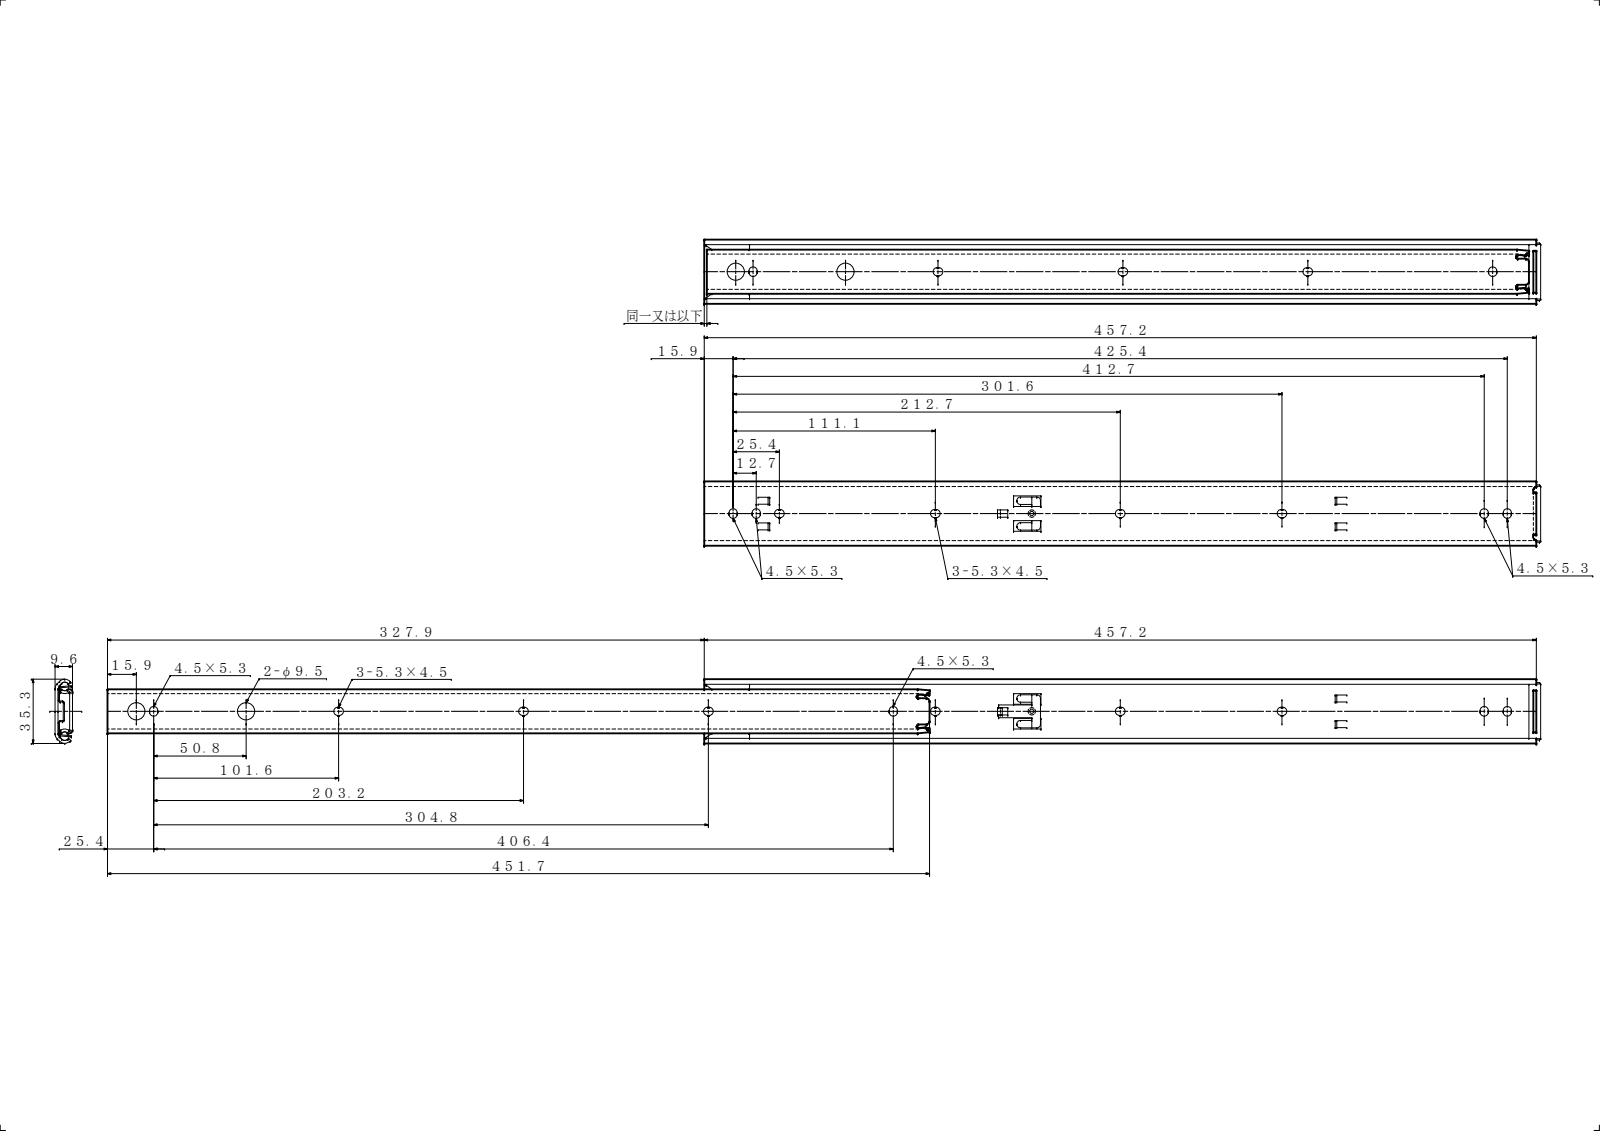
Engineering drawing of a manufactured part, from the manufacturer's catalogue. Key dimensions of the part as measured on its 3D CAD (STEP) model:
Part name (STEP PRODUCT): PN1; PN84 ol; S103-18; PN101リベット (+3 more)
STEP written by: SolidWorks 2019 (CONFIG_CONTROL_DESIGN)
Units: millimetres
Bodies: 6 solids, 333 faces (165 planar, 156 cylindrical, 12 other)
Overall size (bounding box): 787.5 × 35.3 × 9.6
Volume: 58 820 mm³ · Surface area: 77 890 mm²
Round holes (diameter × count): ⌀9.5 ×2, ⌀2.4 ×1, ⌀2.6 ×1, ⌀4.2 ×1
Round bosses / shafts (diameter × count): ⌀4.6 ×2, ⌀2.3 ×1
Partial cylindrical surfaces — rounded edges, fillets, slot ends (radius × count): R2.25 ×30, R0.2 ×22, R0.3 ×10, R0.5 ×6, R0.8 ×6, R2 ×6, R3 ×6, R0.1 ×4
Main face-to-face distances: 1.6, 8, 6.4, 9.6, 5.1, 1.3, 4.67, 3.07, 2.9, 6.7
Hole centre spacings: 60.3, 431.65, 491.95
